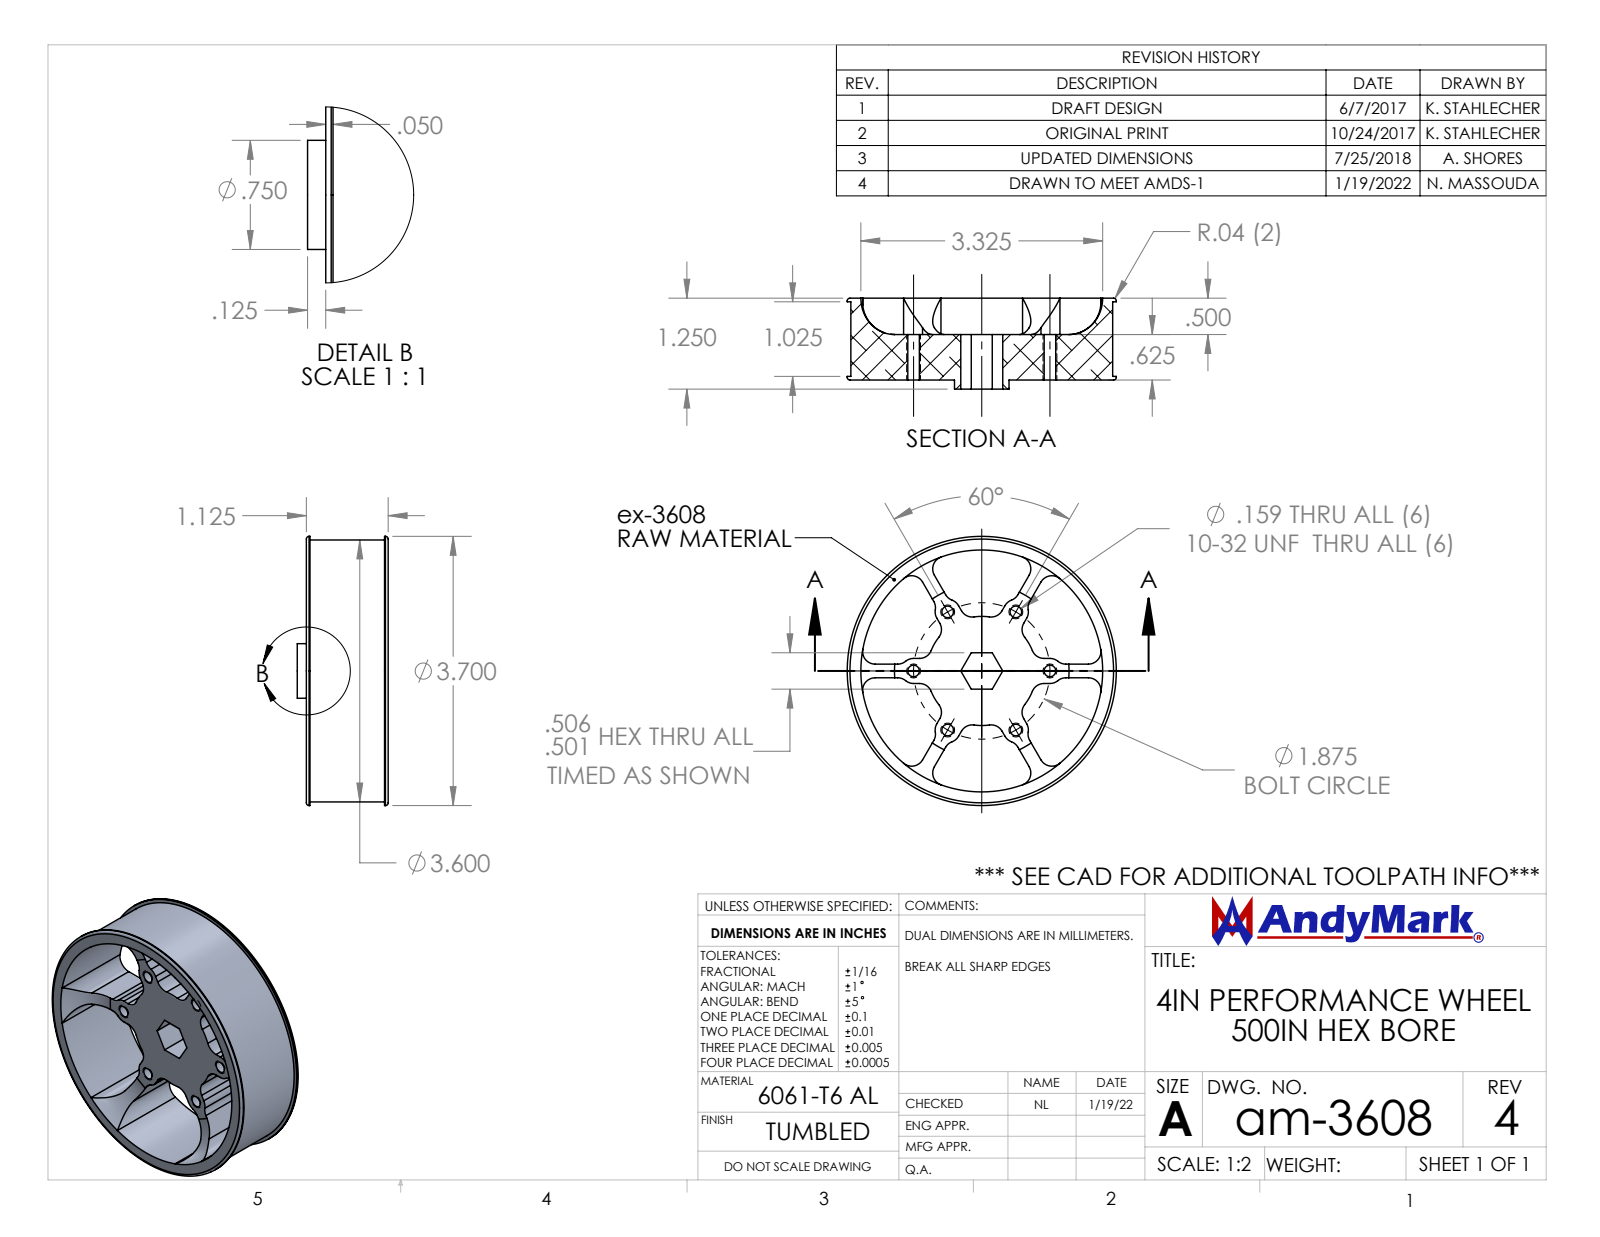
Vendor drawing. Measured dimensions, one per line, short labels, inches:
name: 4IN Extrusion Performance Wheel 500 hex
written by: SolidWorks 2021 (CONFIG_CONTROL_DESIGN)
unit: in
bodies: 1 solid, 136 faces (36 planar, 90 cylindrical, 10 other)
size: 3.7 × 3.7 × 1.25
volume: 3.654 in³; area: 45.7 in²
holes: 6× ⌀0.159
bosses: 1× ⌀3.7, 1× ⌀3.6, 1× ⌀0.75
rounds: 42× R0.172, 1× R0.75, 1× R1.662, 1× R1.663
face distances: 0.5, 0.625, 1.125, 0.156, 0.344, 0.187, 0.05, 1.075, 0.575, 1.025
hole spacings: 1.624, 0.937, 1.875, 0.938
